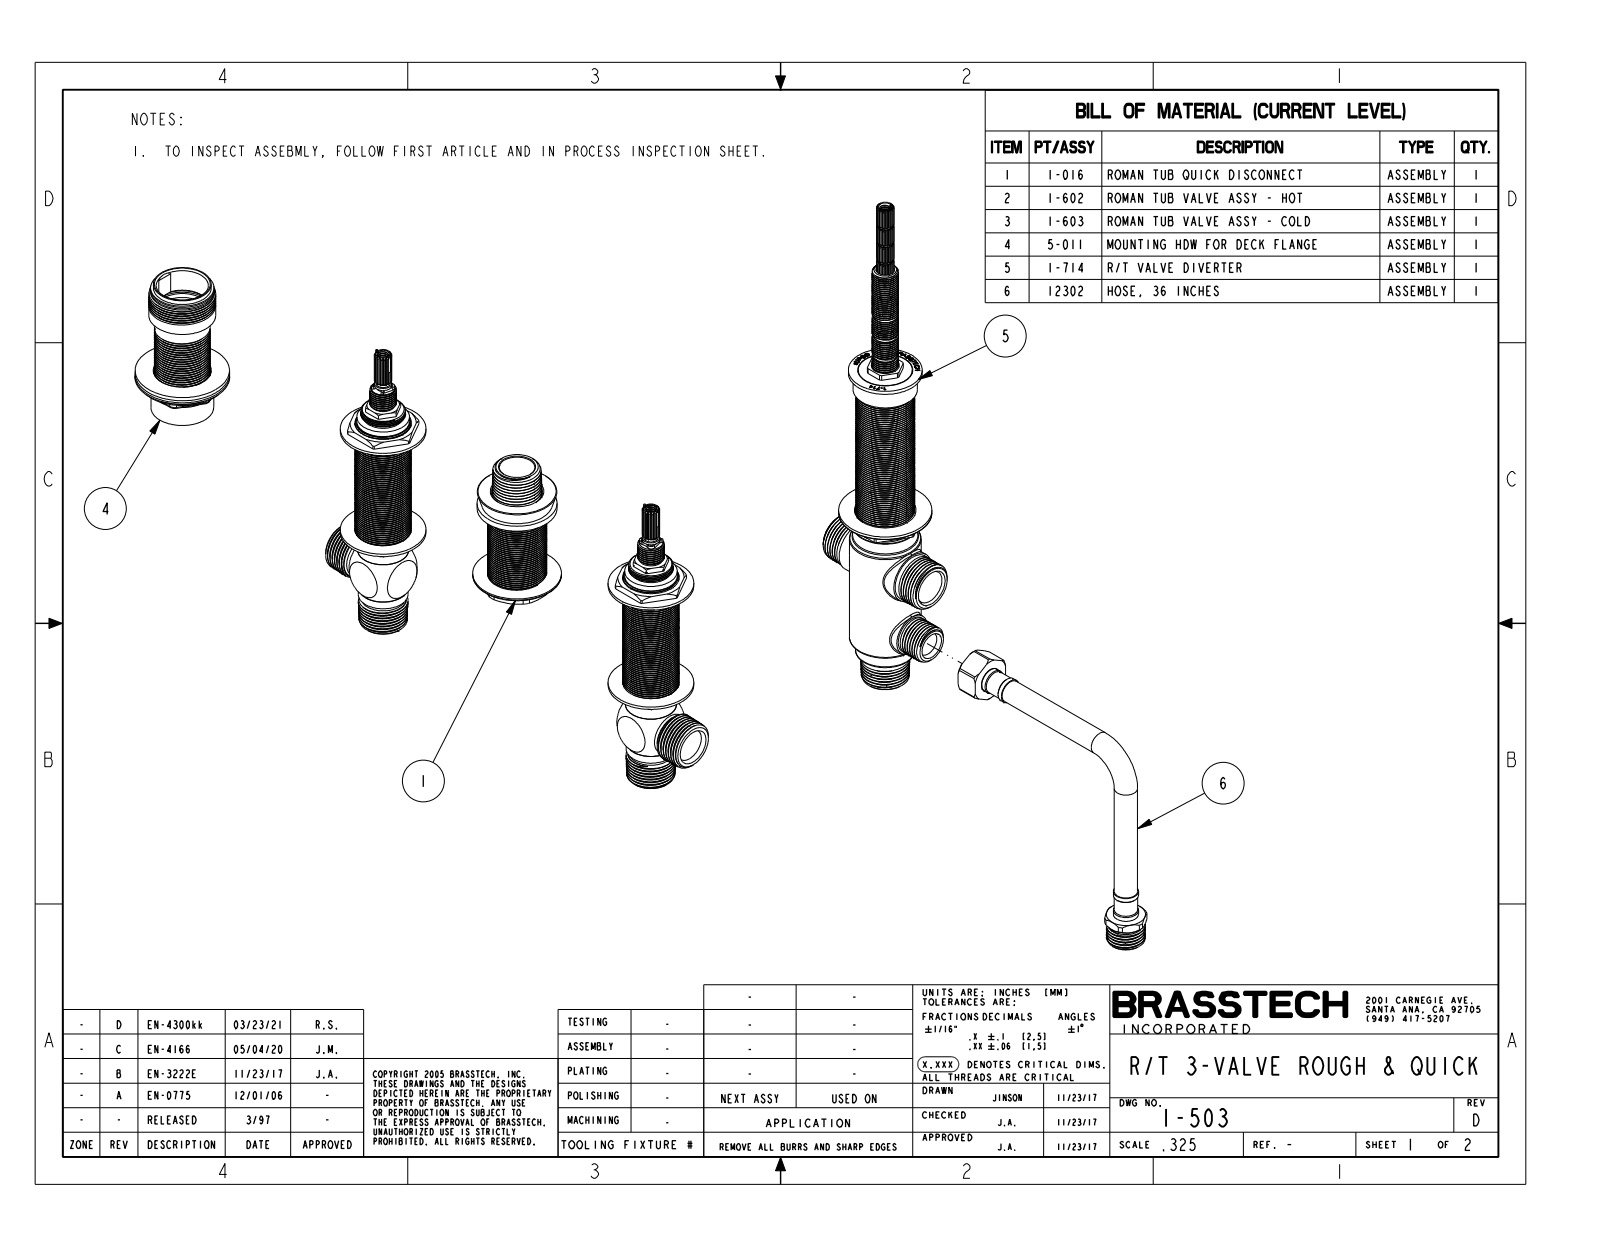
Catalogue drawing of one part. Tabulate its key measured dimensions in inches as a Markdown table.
| quantity | value |
| --- | --- |
| part name | 10173; 91083; 10172; 10174 (+8 more) |
| STEP written by | CREO PARAMETRIC BY PTC INC, 2018400 (AUTOMOTIVE_DESIGN) |
| units | inches |
| bodies | 34 solids, 4022 faces (904 planar, 1674 cylindrical, 1444 other) |
| overall size | 19.156 × 15.404 × 10.984 |
| volume | 32.43 in³ |
| surface area | 363.7 in² |
| round holes (diameter × count) | 0.196 × 2, 0.201 × 2, 0.236 × 2, 0.276 × 2, 0.394 × 2, 1.11 × 2, 0.138 × 1, 0.202 × 1, 0.274 × 1, 0.393 × 1, 0.417 × 1, 0.447 × 1 |
| round bosses / shafts (diameter × count) | 0.043 × 4, 1.811 × 2, 1.187 × 2, 1.11 × 2, 1.099 × 2, 1.047 × 2, 0.945 × 2, 0.929 × 2 |
| partial cylindrical surfaces (radius × count) | 0.04 × 15, 0.08 × 8, 0.039 × 6, 0.15 × 6, 0.164 × 3, 0.06 × 2, 0.187 × 2, 0.26 × 2 |
| main face-to-face distances | 0.061, 1.602, 1.85, 0.248, 0.04, 2.613, 2.573, 0.039, 1.563, 1.811 |
| hole center spacings | 4, 9.22, 1.496, 5.703, 6, 8, 9.732, 10 |
